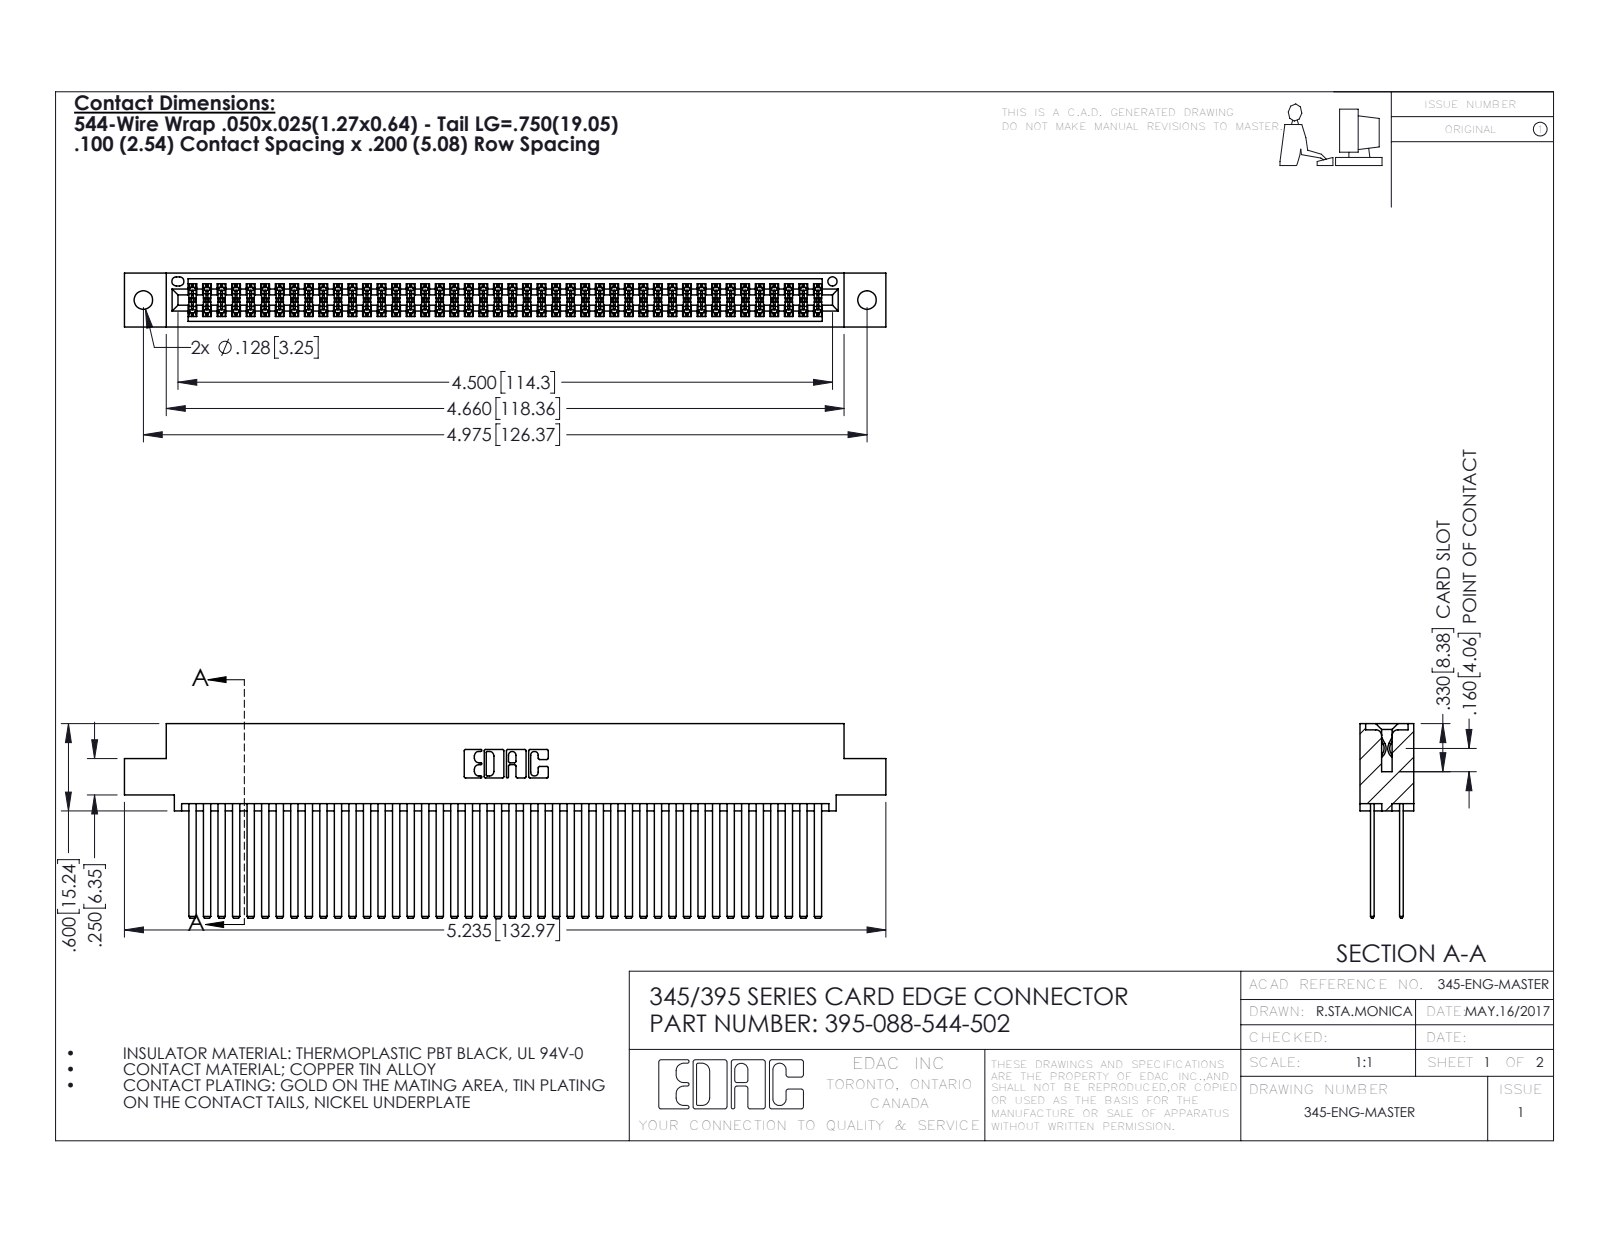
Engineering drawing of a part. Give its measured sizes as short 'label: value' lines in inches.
name: 345 Part_0.110 Offset - 0.128 Dia; 345-292-001_345-293-144; 395-088-544-502
written by: SolidWorks 2016 (CONFIG_CONTROL_DESIGN)
unit: in
bodies: 89 solids, 4002 faces (2636 planar, 1366 cylindrical, 0 other)
size: 5.235 × 1.337 × 0.37
volume: 0.858 in³; area: 37.6 in²
holes: 2× ⌀0.128, 1× ⌀0.064
rounds: 132× R0.006, 22× R0.01, 6× R0.007, 6× R0.031, 3× R0.026, 2× R0.014, 2× R0.019, 2× R0.022
face distances: 0.2, 0.025, 0.298, 0.072, 0.098, 0.272, 0.225, 0.175, 0.37, 0.05
hole spacings: 0.27, 4.739, 4.975
